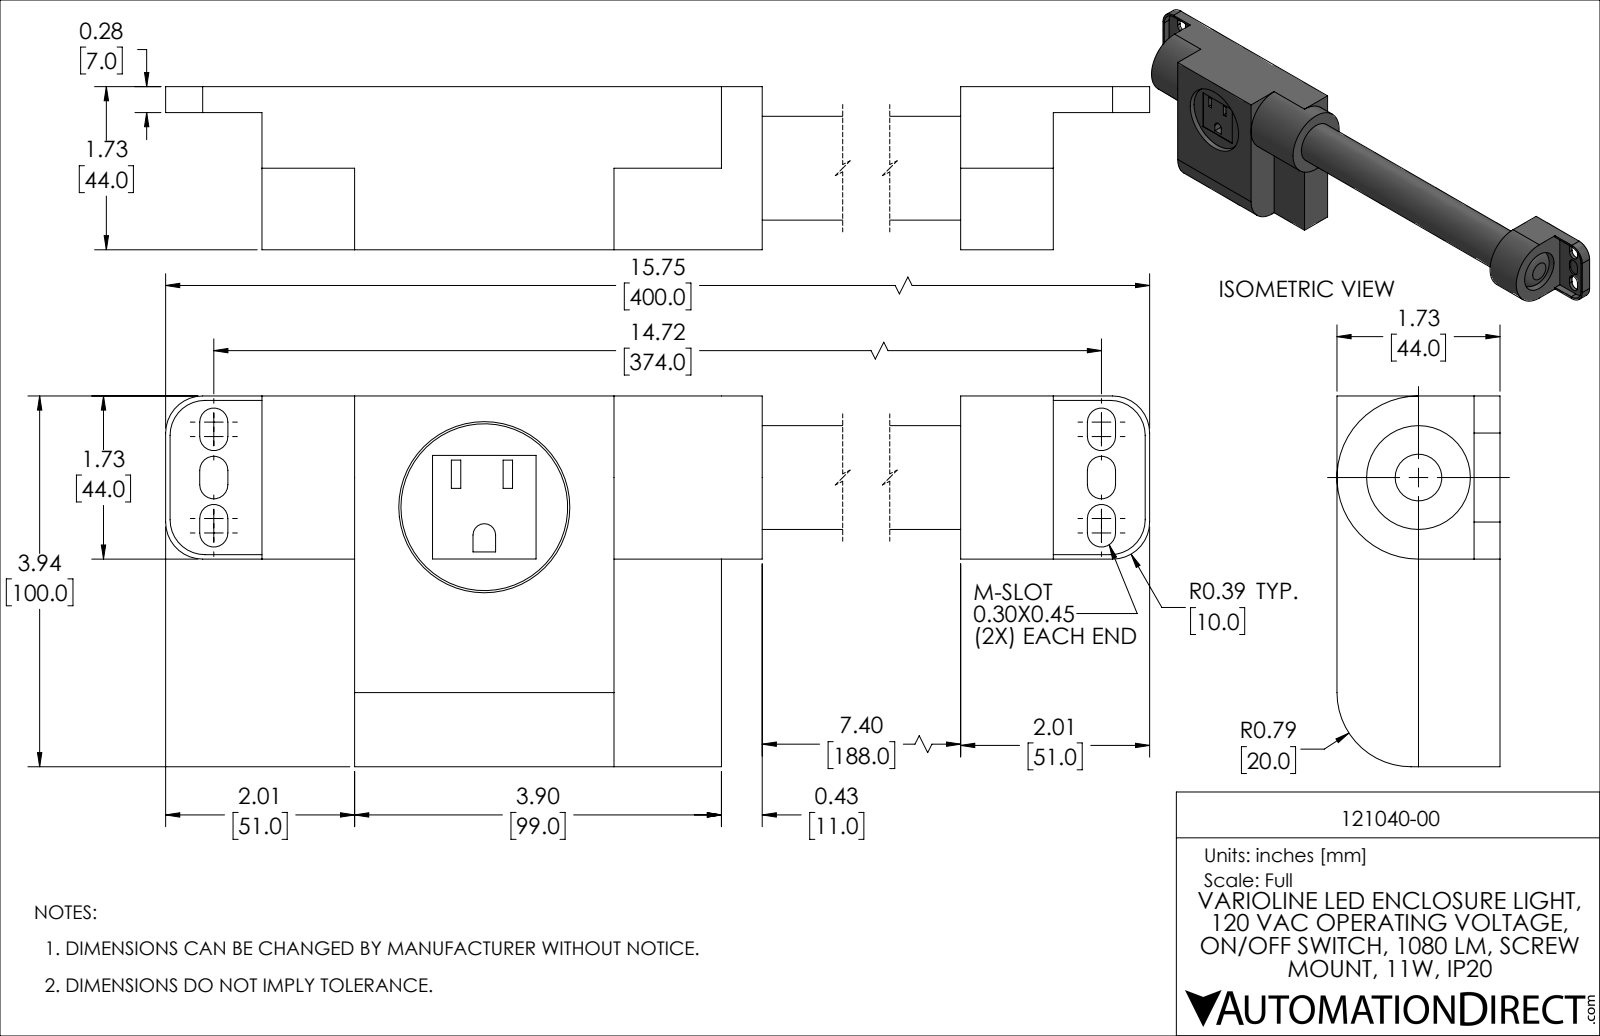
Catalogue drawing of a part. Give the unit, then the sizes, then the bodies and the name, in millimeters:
Units: millimetres
Overall size (bounding box): 400 × 100 × 44
Round holes (diameter × count): ⌀28 ×1, ⌀46.15 ×1
Round bosses / shafts (diameter × count): ⌀45 ×1, ⌀44 ×1
Partial cylindrical surfaces — rounded edges, fillets, slot ends (radius × count): R3.8 ×12, R9.4 ×4, R10 ×4, R3.05 ×1, R20 ×1
Main face-to-face distances: 44, 22, 100, 323, 25, 41.6, 2.4, 19.6, 99, 70
Volume: 601 528 mm³ · Surface area: 80 543 mm²
Bodies: 1 solid, 113 faces (69 planar, 38 cylindrical, 6 other)
Part name (STEP PRODUCT): PRODUCT_NAME_1
STEP written by: ACIS (AUTOMOTIVE_DESIGN_CC2)
